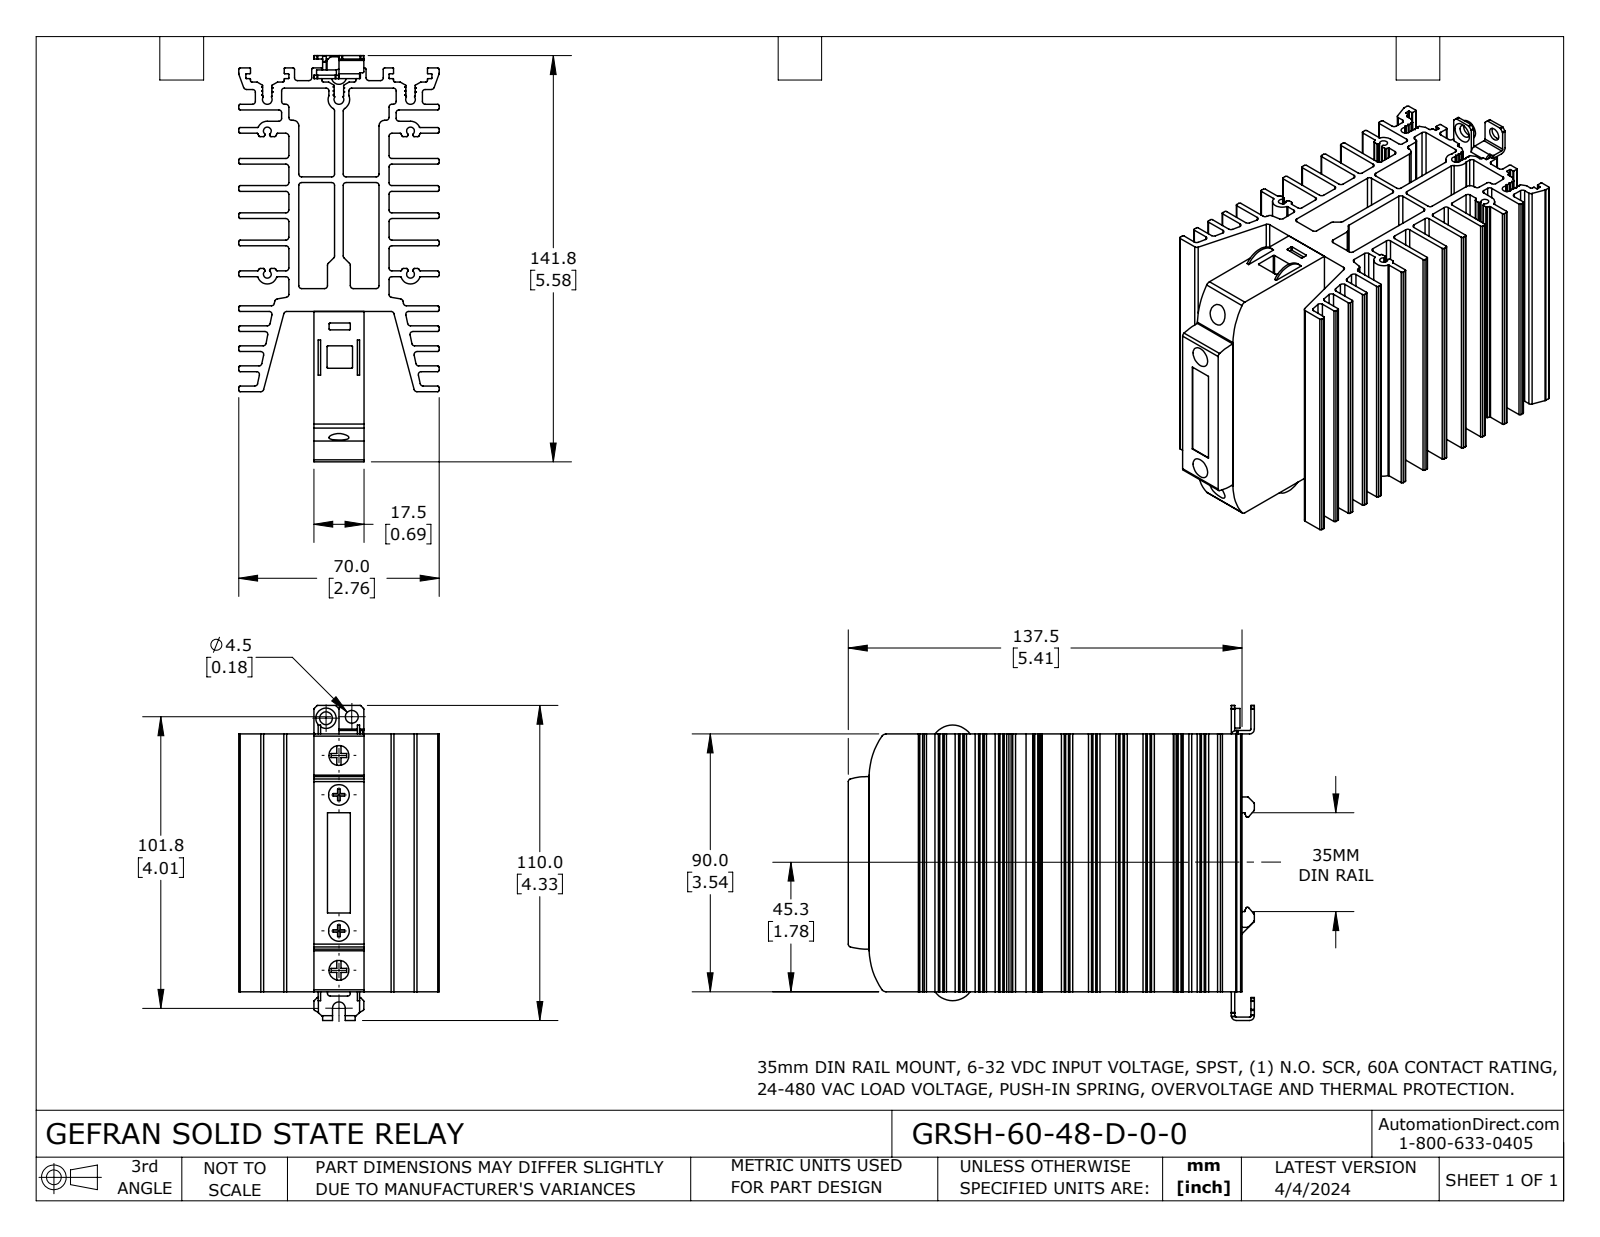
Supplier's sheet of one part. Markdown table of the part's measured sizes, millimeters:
| quantity | value |
| --- | --- |
| part name | GRSH-60-48-D-0-0 |
| STEP written by | SolidWorks 2023 (CONFIG_CONTROL_DESIGN) |
| units | millimeters |
| bodies | 4 solids, 965 faces (511 planar, 452 cylindrical, 2 other) |
| overall size | 141.8 × 110 × 70 |
| volume | 283 000 mm³ |
| surface area | 165 300 mm² |
| round holes (diameter × count) | 4.5 × 2, 7 × 2, 7.2 × 2 |
| round bosses / shafts (diameter × count) | 6.9 × 1, 5.2 × 1 |
| partial cylindrical surfaces (radius × count) | 1 × 98, 0.5 × 75, 0.2 × 64, 0.4 × 58, 0.3 × 40, 1.7 × 10, 0.1 × 6, 1.4 × 4 |
| main face-to-face distances | 19, 2, 9.5, 12.5, 26.2, 11.5, 5.3, 22.8, 7.5, 15.5 |
| hole center spacings | 13.7, 61.2, 9, 13.8, 14.2, 27.1, 27.6, 47.5 |
